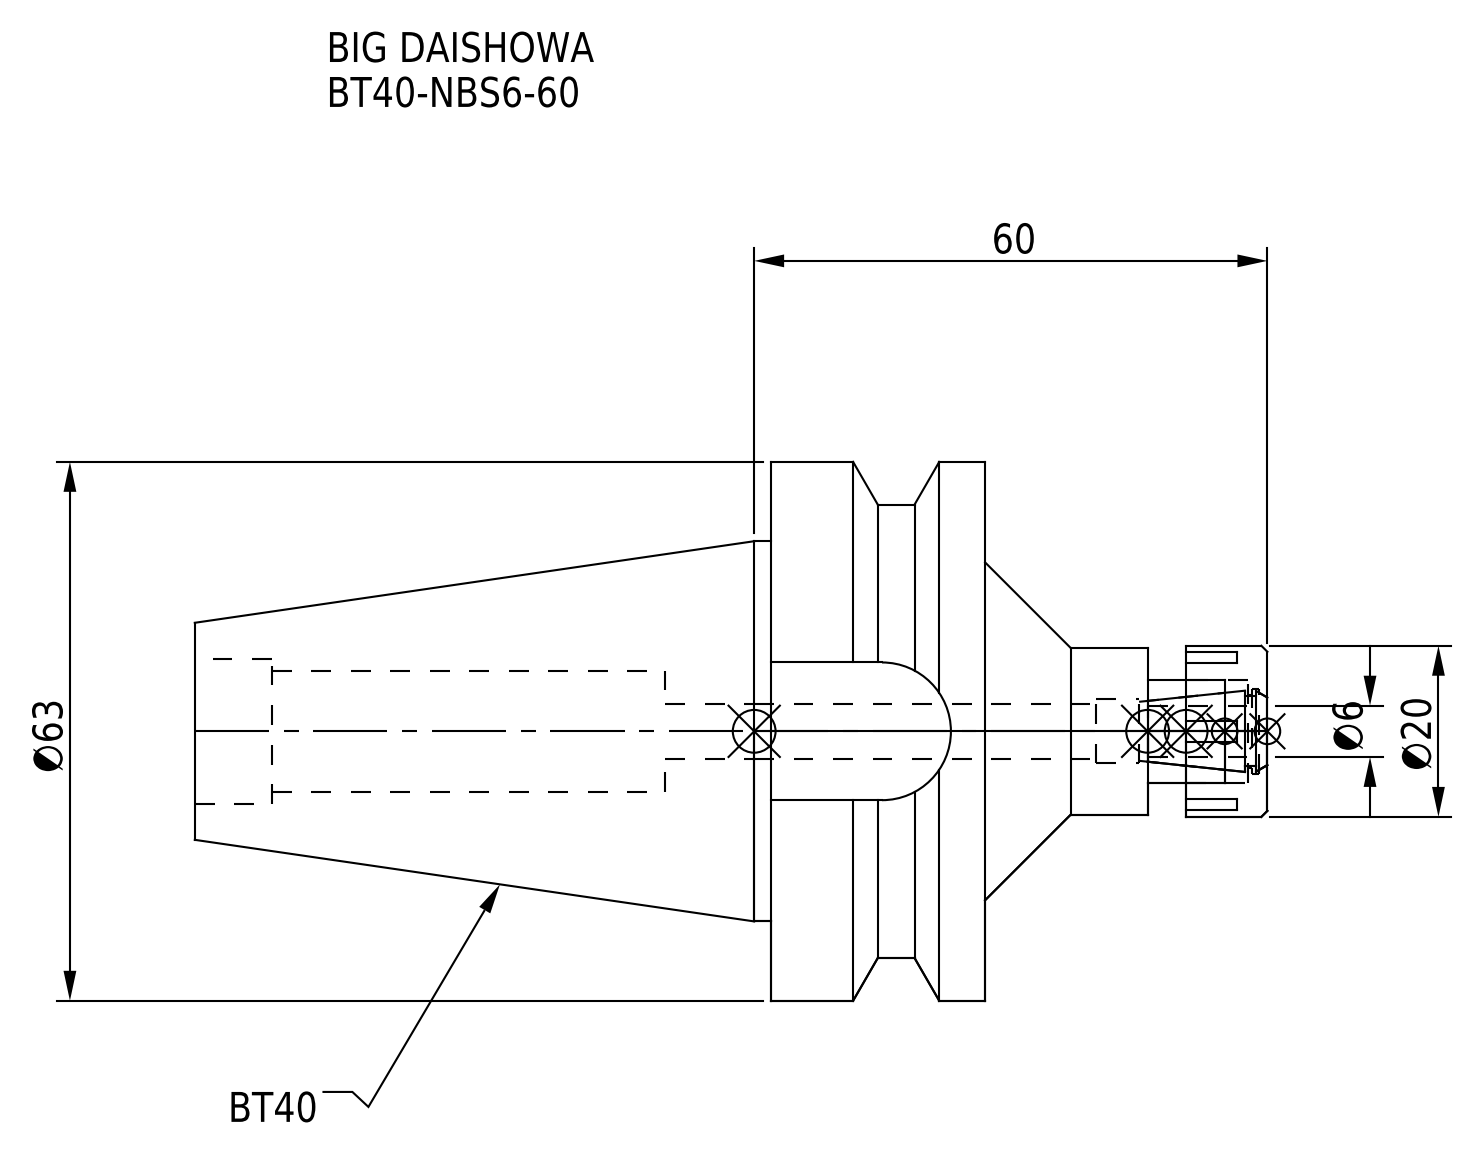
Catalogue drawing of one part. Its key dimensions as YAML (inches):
part_name: "BT40-NBS6-60.stp; BT40-NBS6-60; BT40-NBS6-60_1.stp; DXF_TEMP_ASSY_ASM_4_ASM.stp (+3 more)"
step_written_by: "SolidWorks 2019 (CONFIG_CONTROL_DESIGN)"
units: inches
bodies: {solids: 2, faces: 90, planar: 44, cylindrical: 32, other: 14}
overall_size: [4.937, 2.48, 2.48]
volume: 8.257
surface_area: 39.38
round_holes:
  - {diameter: 0.252, count: 1}
  - {diameter: 0.295, count: 1}
  - {diameter: 0.335, count: 1}
  - {diameter: 0.394, count: 1}
  - {diameter: 0.472, count: 1}
  - {diameter: 0.559, count: 1}
  - {diameter: 0.669, count: 1}
round_bosses_or_shafts:
  - {diameter: 2.48, count: 1}
  - {diameter: 2.087, count: 1}
  - {diameter: 1.75, count: 1}
  - {diameter: 0.787, count: 1}
  - {diameter: 0.768, count: 1}
partial_cylinders:
  - {radius: 0.317, count: 1}
face_to_face_distances: [0.984, 1.772, 3.638, 2.654, 4.386, 0.177, 1.299, 2.283, 4.937, 0.551]
